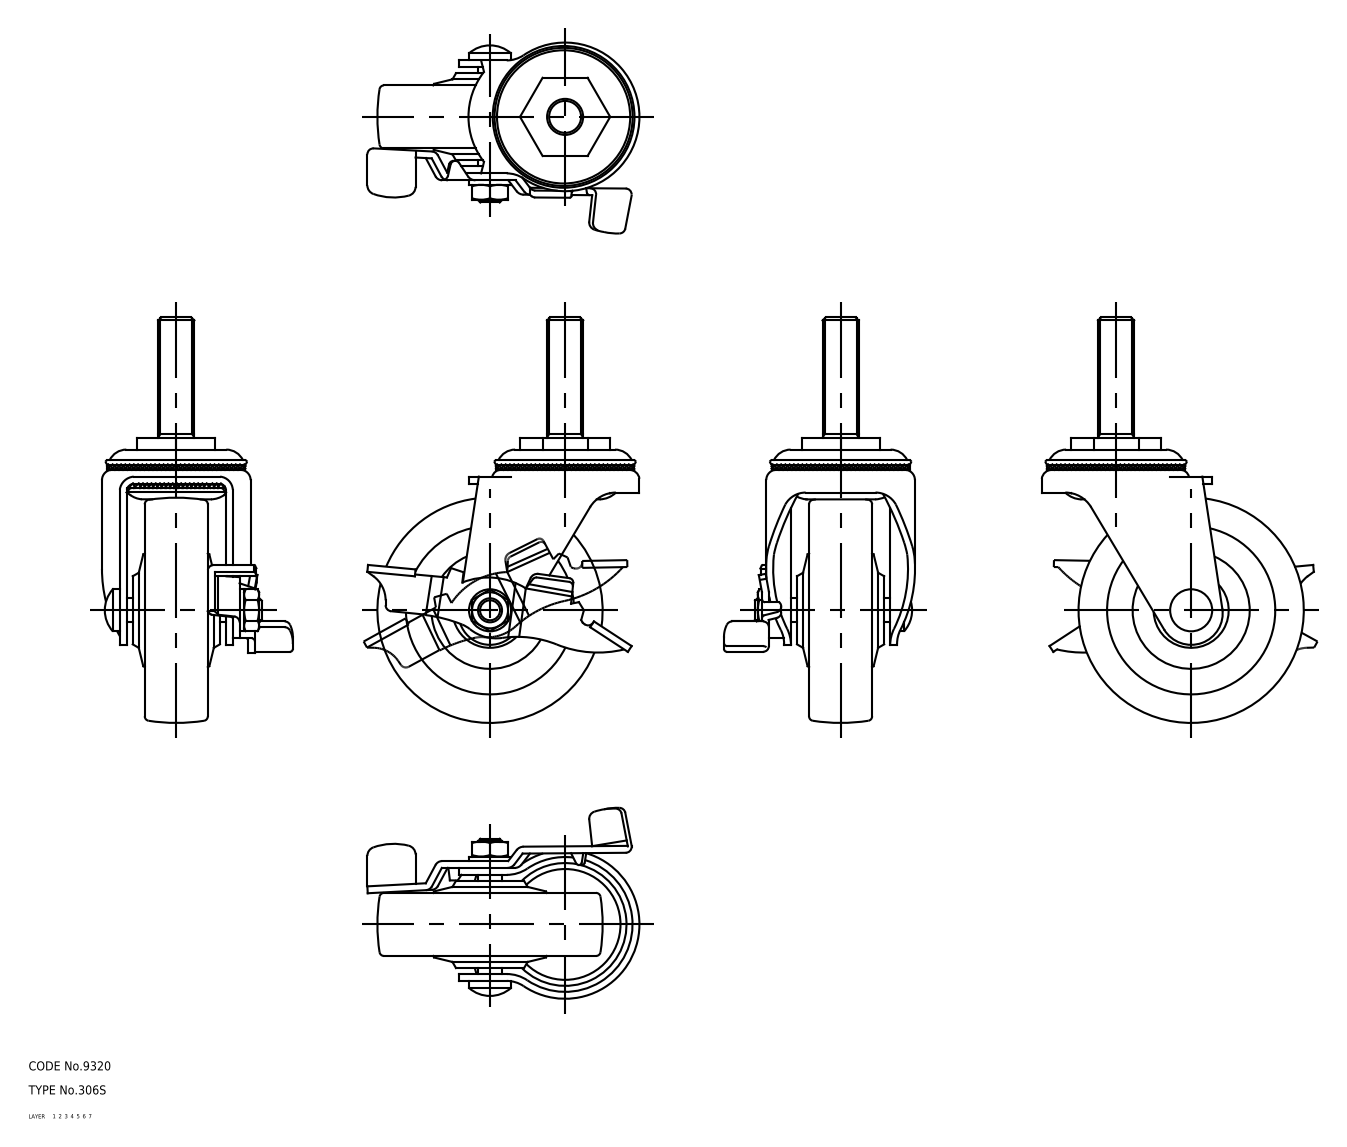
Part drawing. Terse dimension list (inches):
name: 67127149; 67127162; 67127175; 67127188 (+1 more)
written by: CADfix (AUTOMOTIVE_DESIGN)
unit: in
bodies: 5 solids, 259 faces (0 planar, 0 cylindrical, 259 other)
size: 5.315 × 3.567 × 2.503
volume: 8.414 in³; area: 58.81 in²
